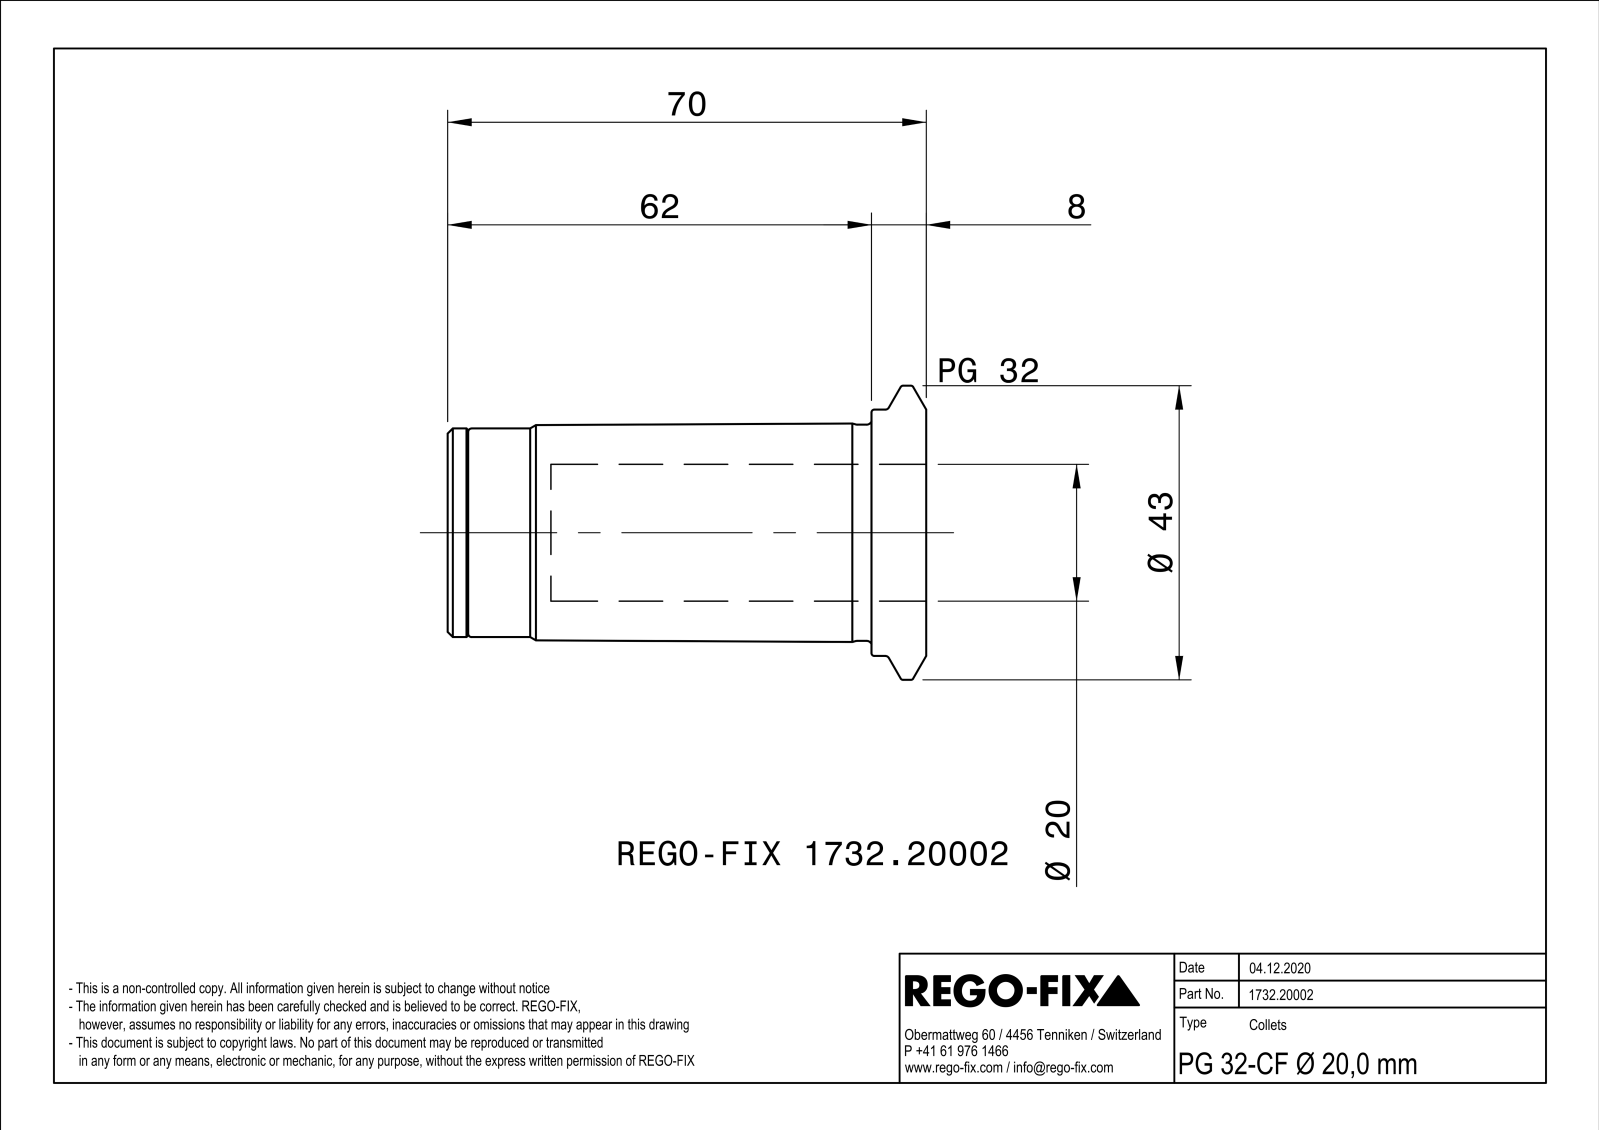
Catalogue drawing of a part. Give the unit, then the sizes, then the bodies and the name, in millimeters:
Units: millimetres
Overall size (bounding box): 70 × 43 × 42.99
Round holes (diameter × count): ⌀4 ×3, ⌀8.92 ×1, ⌀10.5 ×1, ⌀20 ×1, ⌀26.92 ×1, ⌀28.5 ×1
Round bosses / shafts (diameter × count): ⌀43 ×1, ⌀36 ×1, ⌀31.6 ×1, ⌀30.5 ×1, ⌀26.5 ×1, ⌀21 ×1
Partial cylindrical surfaces — rounded edges, fillets, slot ends (radius × count): R2 ×6, R1 ×3, R3.5 ×3, R3.98 ×1, R4.75 ×1, R8.75 ×1
Main face-to-face distances: 1, 70, 58, 12, 59, 11, 8, 60, 2, 10
Hole centre spacings: 7.75, 13.42, 13.43
Volume: 35 776 mm³ · Surface area: 16 740 mm²
Bodies: 1 solid, 130 faces (31 planar, 45 cylindrical, 54 other)
Part name (STEP PRODUCT): NOCUT
STEP written by: SIEMENS PLM Software Solid Edge ST10 (AUTOMOTIVE_DESIGN)
